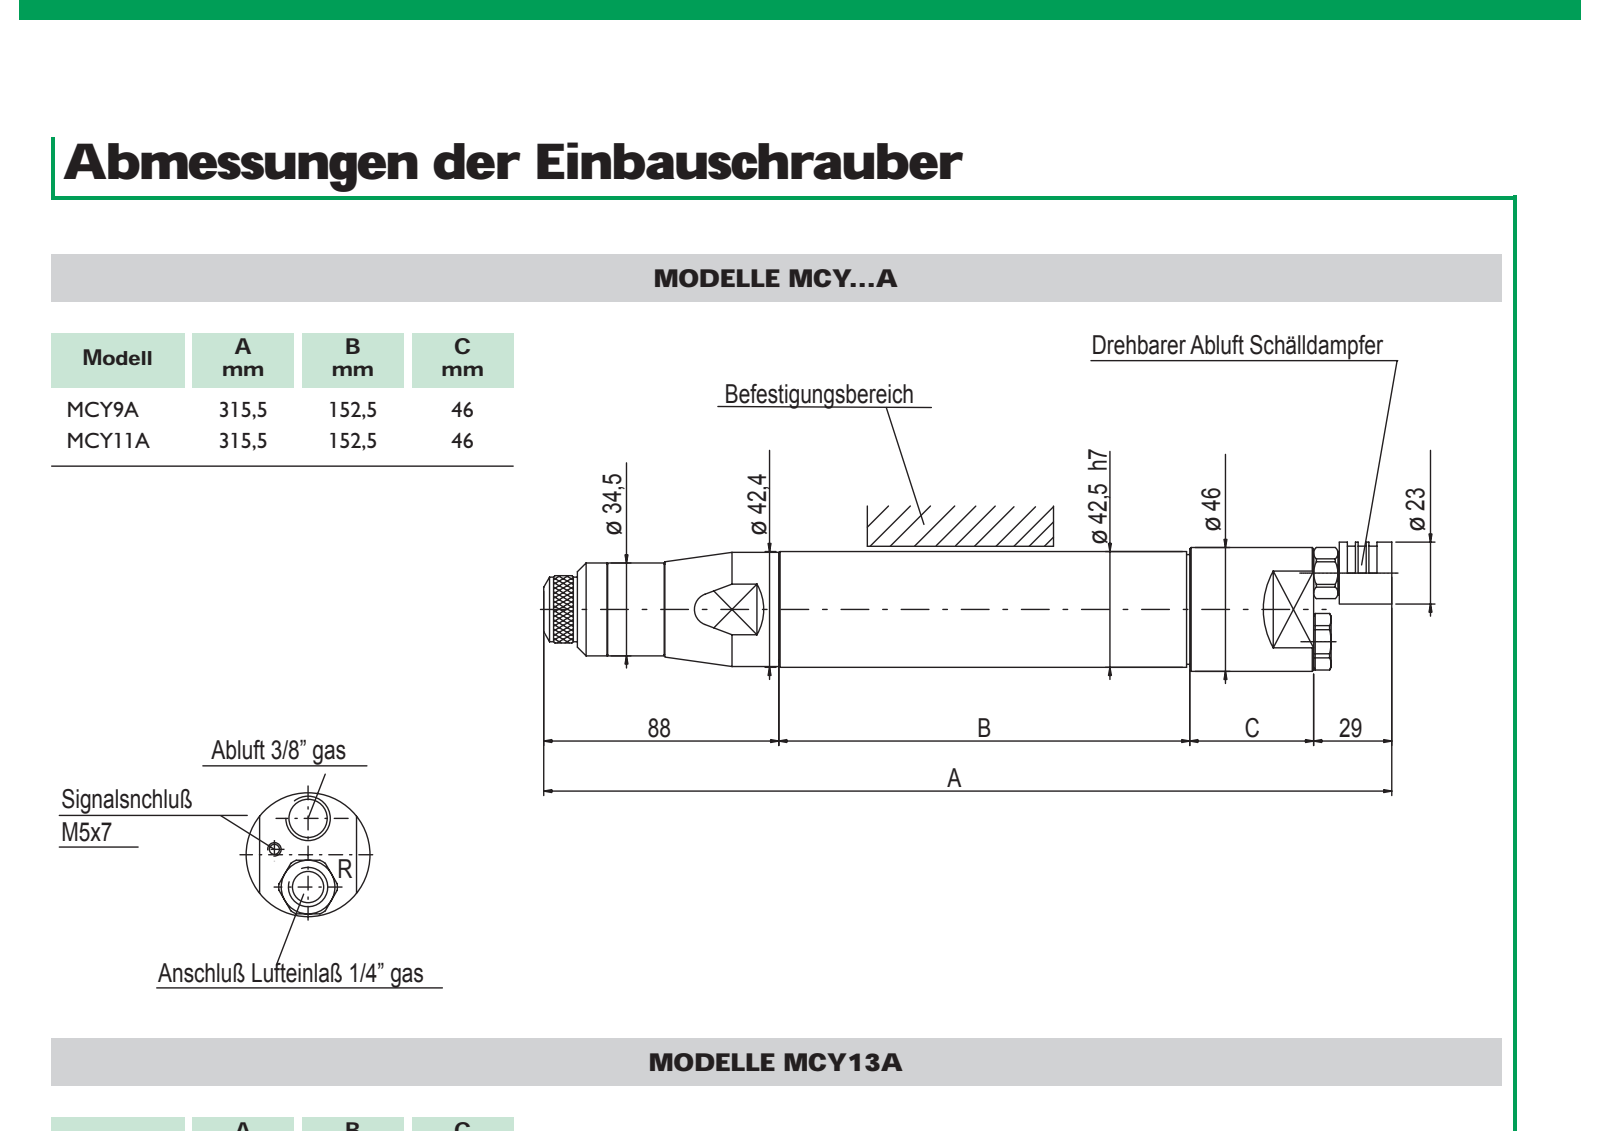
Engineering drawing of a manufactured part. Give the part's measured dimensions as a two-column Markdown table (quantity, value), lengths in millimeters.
| quantity | value |
| --- | --- |
| part name | MCY9_11_1 |
| STEP written by | Autodesk Inventor 2013 (AUTOMOTIVE_DESIGN) |
| units | millimeters |
| bodies | 0 solids, 217 faces (62 planar, 112 cylindrical, 43 other) |
| overall size | 286.4 × 49.51 × 48.03 |
| round holes (diameter × count) | 5 × 10, 1.5 × 2, 15 × 2, 16.66 × 2, 10 × 1, 12 × 1, 12.6 × 1, 14.6 × 1, 15.25 × 1, 16.5 × 1, 18.6 × 1, 20 × 1 |
| round bosses / shafts (diameter × count) | 1 × 25, 23 × 1, 19.85 × 1, 16 × 1, 15.9 × 1, 14.15 × 1, 14 × 1, 13.3 × 1 |
| partial cylindrical surfaces (radius × count) | 1.6 × 4, 1.5 × 2, 8.5 × 1, 10.5 × 1, 31.5 × 1 |
| main face-to-face distances | 25, 1.5, 16, 14.5, 26.5, 30, 25.9, 12.5, 9, 10.5 |
| hole center spacings | 8.5, 7.23, 13.5, 14, 18.41, 22.1, 27.5, 31.11 |
